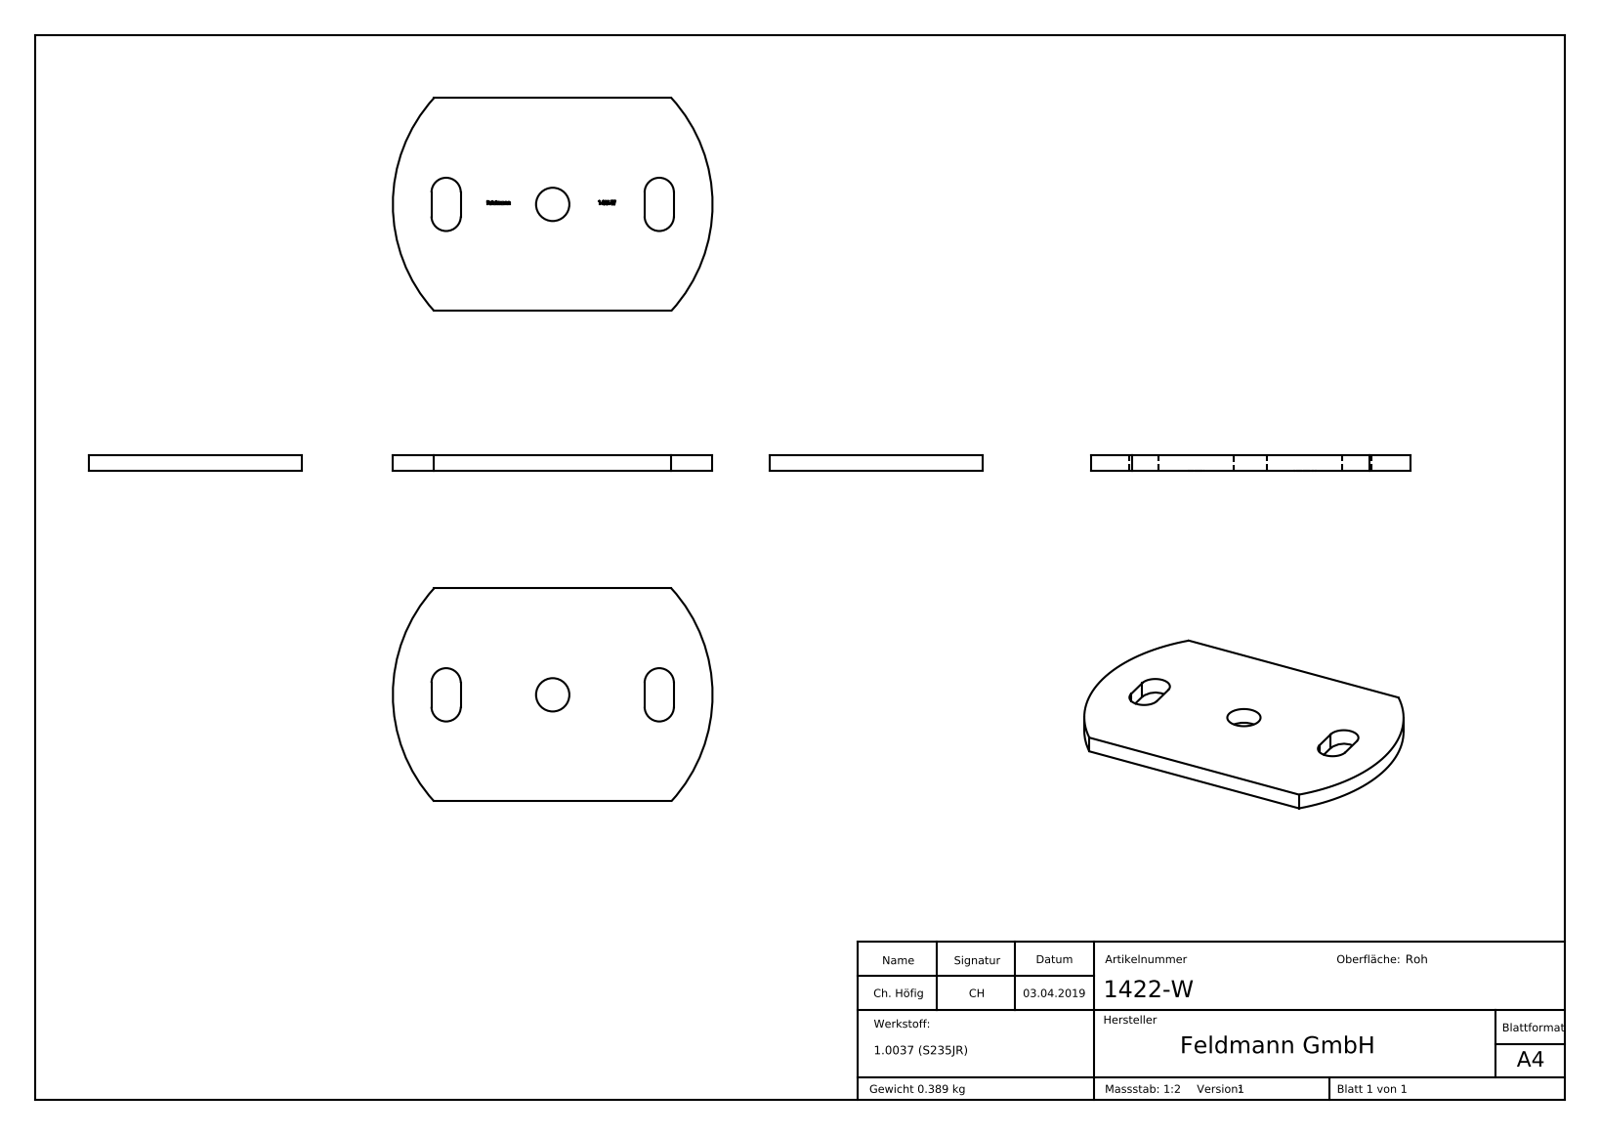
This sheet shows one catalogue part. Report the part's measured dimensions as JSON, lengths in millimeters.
{"part_name": "1422-W", "step_written_by": "SolidWorks 2015 (CONFIG_CONTROL_DESIGN)", "units": "millimeters", "bodies": {"solids": 1, "faces": 198, "planar": 128, "cylindrical": 10, "other": 60}, "overall_size": [120, 80, 6], "volume_mm3": 49867, "surface_area_mm2": 19618, "round_holes": [[12.5, 1]], "partial_cylinders_radius": [[5.5, 4], [59.36, 2]], "face_to_face_distances": [6, 80, 11, 91, 69, 5.9, 40, 0.44, 40.28, 2.02]}
